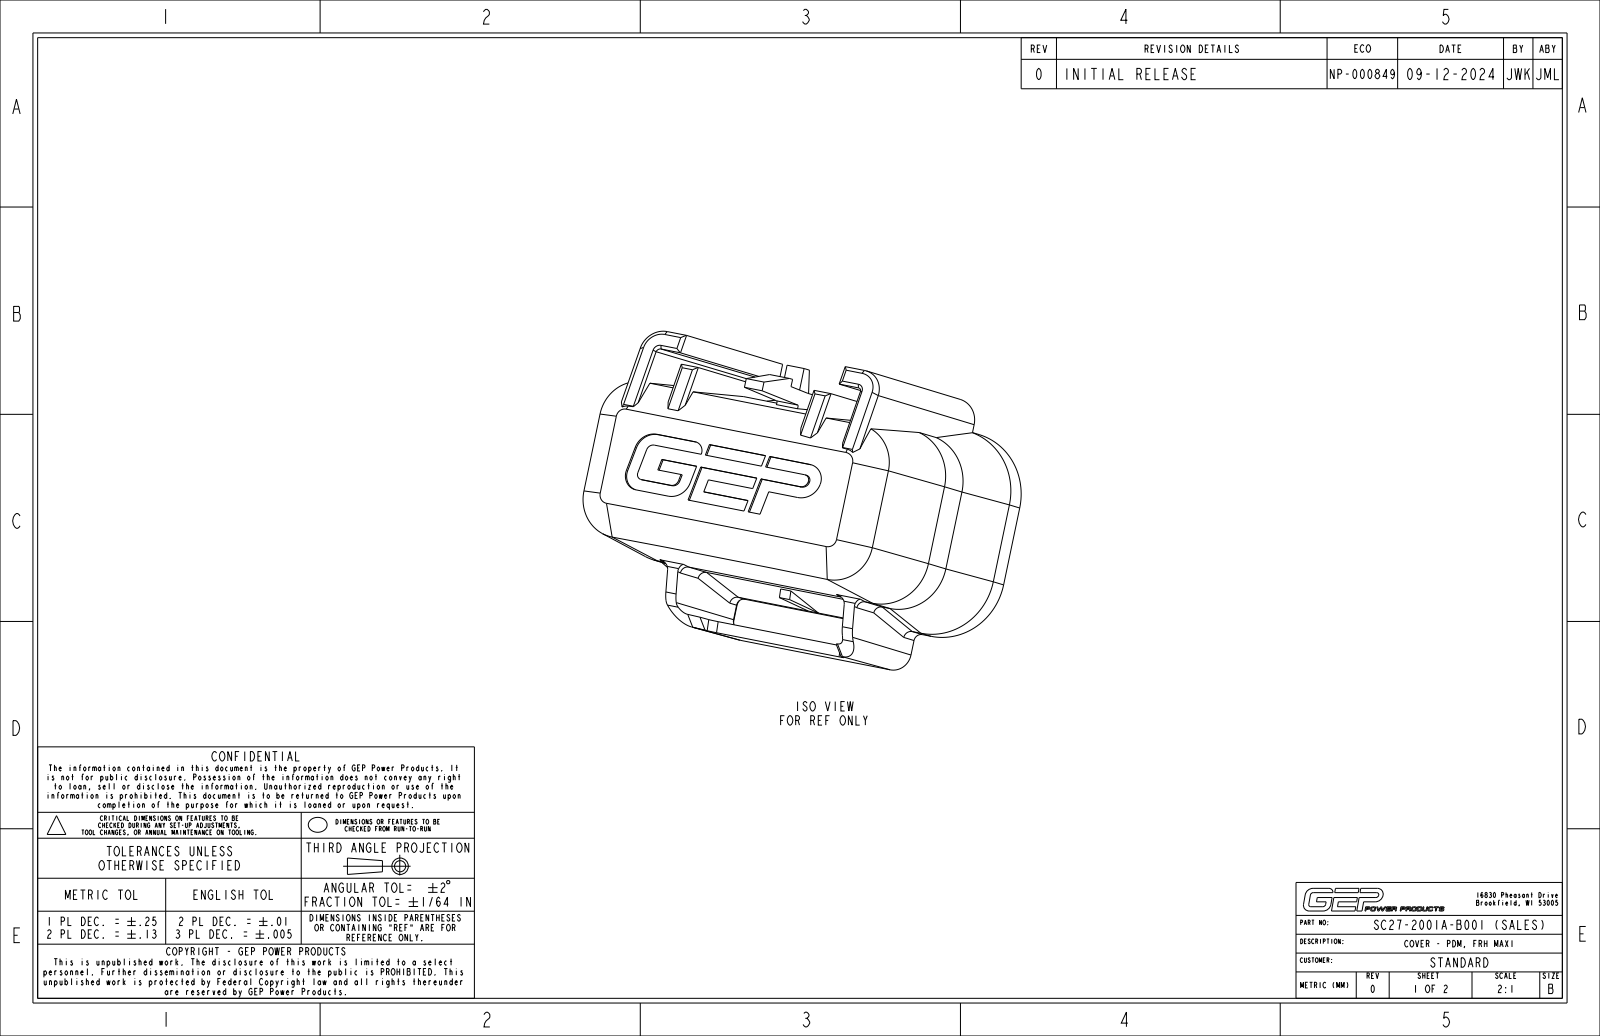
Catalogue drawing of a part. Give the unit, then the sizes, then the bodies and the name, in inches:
Units: inches
Overall size (bounding box): 1.929 × 1.89 × 1.483
Partial cylindrical surfaces — rounded edges, fillets, slot ends (radius × count): R0.008 ×46, R0.039 ×24, R0.016 ×4, R0.205 ×4, R0.264 ×4, R0.283 ×4, R0.343 ×4, R0.02 ×3
Main face-to-face distances: 0.059, 0.098, 0.079, 0.138, 0.965, 1.024, 0.827, 0.728, 0.886, 0.669
Volume: 0.827 in³ · Surface area: 26.43 in²
Bodies: 1 solid, 490 faces (224 planar, 133 cylindrical, 133 other)
Part name (STEP PRODUCT): PC27-2001A-B001_NCF; SC27-2001A-B001_NCF_ASM
STEP written by: CREO PARAMETRIC BY PTC INC, 2024014 (CONFIG_CONTROL_DESIGN)
